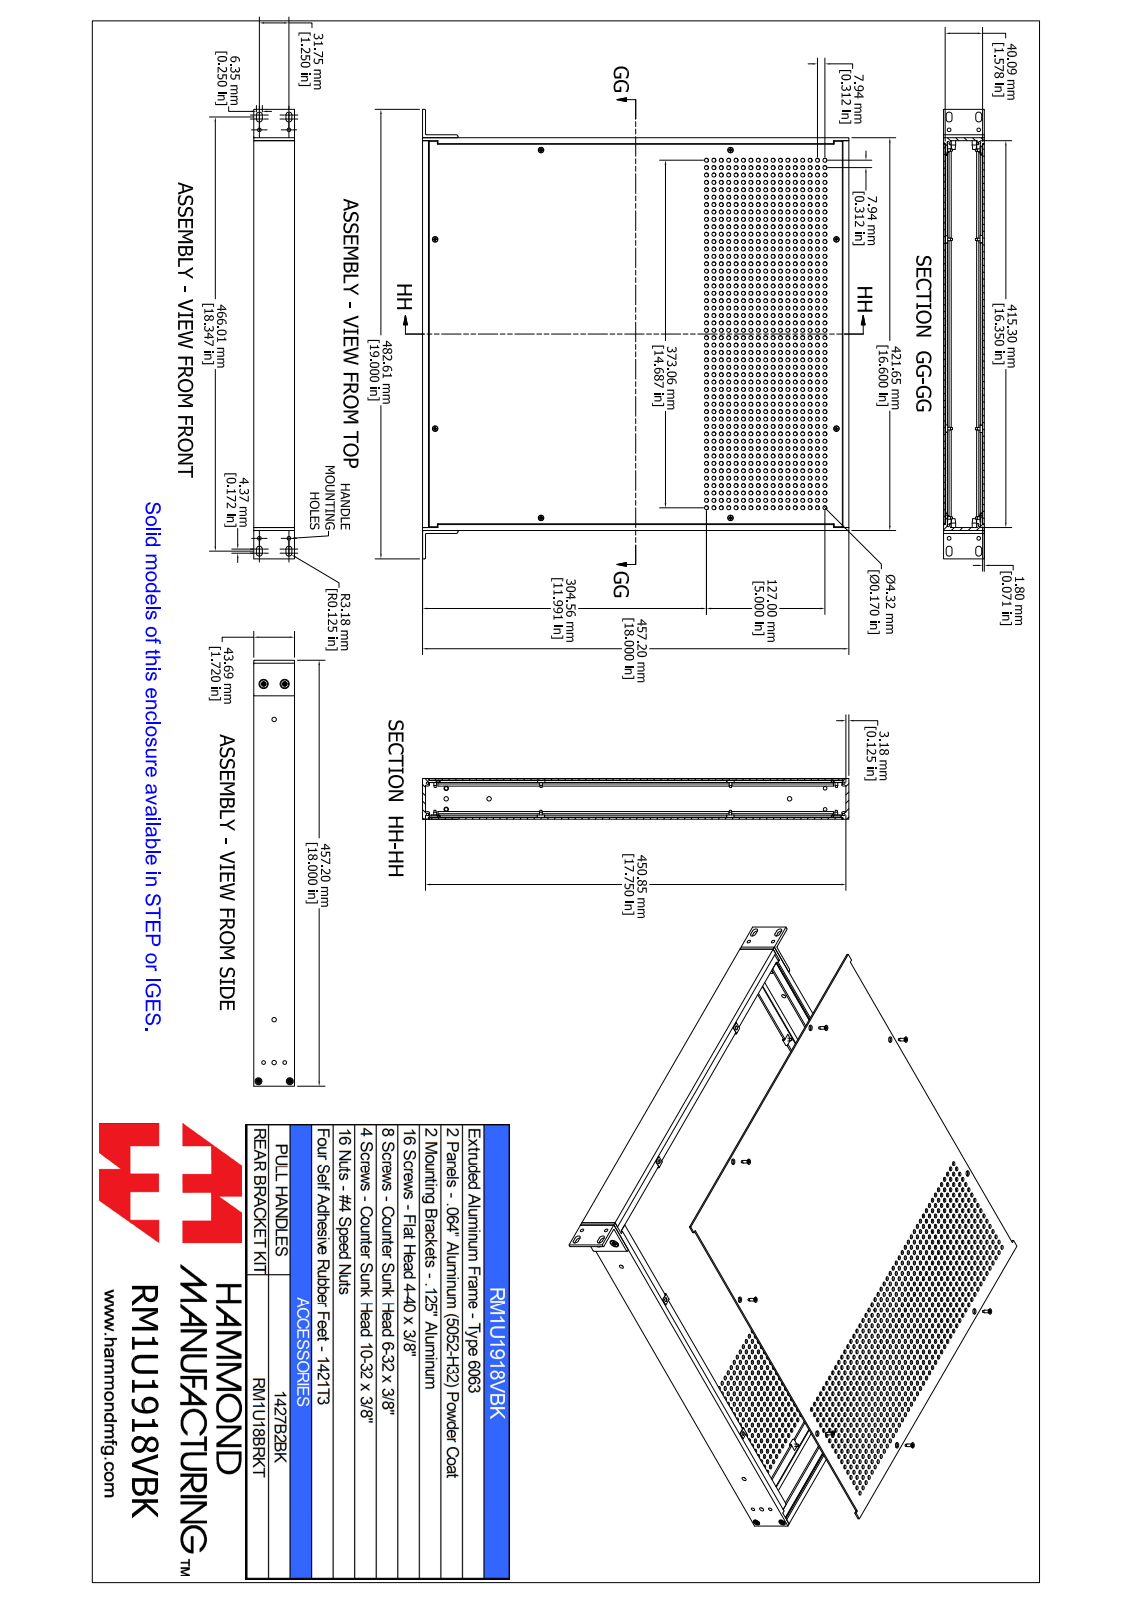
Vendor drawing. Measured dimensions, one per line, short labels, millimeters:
name: RM1U1918VBK
written by: SolidWorks 2021 (AUTOMOTIVE_DESIGN)
unit: mm
bodies: 52 solids, 2990 faces (636 planar, 1858 cylindrical, 496 other)
size: 482.6 × 457.2 × 43.7
volume: 1 016 000 mm³; area: 1 023 000 mm²
holes: 1632× ⌀4.3, 16× ⌀4.5, 12× ⌀4, 8× ⌀2.5, 8× ⌀4.3, 6× ⌀4.8, 4× ⌀4, 4× ⌀4, 2× ⌀5
bosses: 16× ⌀5.4, 16× ⌀2.8, 4× ⌀6, 4× ⌀3.5, 2× ⌀8.5, 2× ⌀4.8
rounds: 20× R1, 16× R3.2, 14× R1.2, 8× R1.3, 6× R1, 4× R0.9, 2× R2
face distances: 1.8, 41.9, 43.7, 40.1, 37.6, 4.2, 39.4, 2.4, 3.2, 0.4
hole spacings: 31.8, 8, 23.8, 63.5, 39.7, 55.5, 15.9, 15.9
